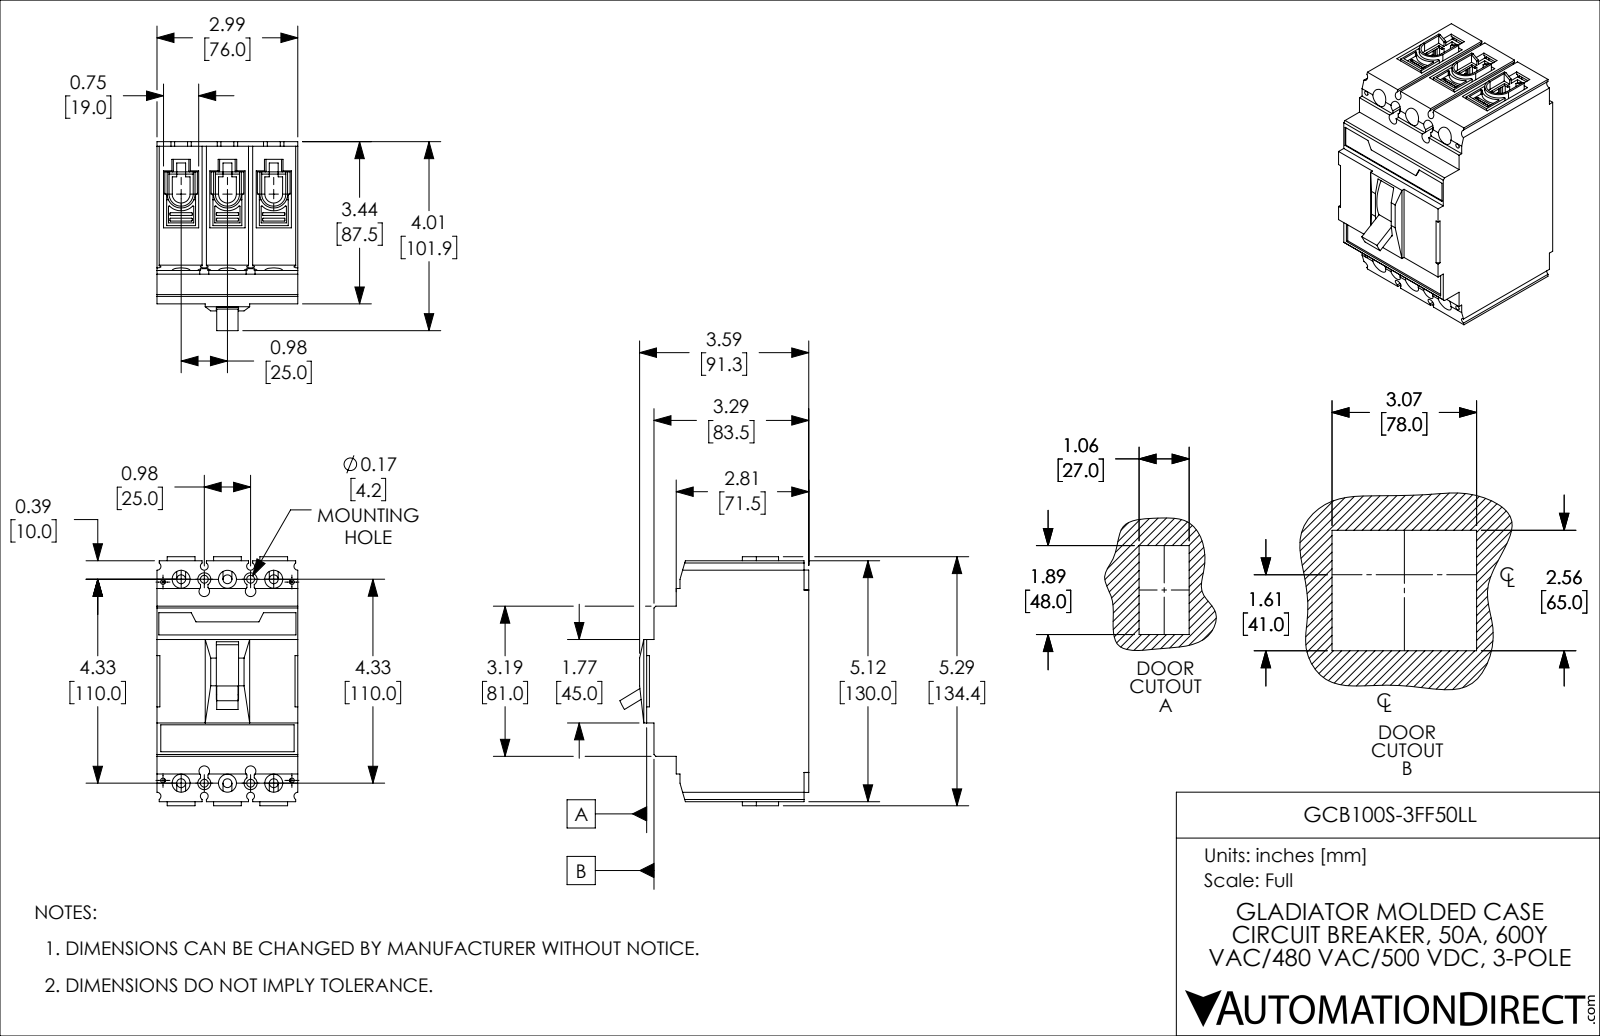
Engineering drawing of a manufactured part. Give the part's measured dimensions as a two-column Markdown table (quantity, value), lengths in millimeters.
| quantity | value |
| --- | --- |
| part name | GCB100S-3FF50LL |
| STEP written by | SolidWorks 2021 (CONFIG_CONTROL_DESIGN) |
| units | millimeters |
| bodies | 1 solid, 1256 faces (784 planar, 424 cylindrical, 48 other) |
| overall size | 134.4 × 101.9 × 76 |
| volume | 708 400 mm³ |
| surface area | 95 810 mm² |
| round holes (diameter × count) | 4.2 × 8, 4.8 × 6, 9.7 × 6, 2.5 × 4, 7 × 4 |
| partial cylindrical surfaces (radius × count) | 0.3 × 86, 0.5 × 38, 1 × 14, 4 × 14, 0.6 × 6, 2.1 × 4, 2.8 × 4, 4.8 × 3 |
| main face-to-face distances | 76, 25, 15.8, 114.2, 44, 2.8, 87.5, 19, 50, 130 |
| hole center spacings | 12.5, 14.3, 25, 110.7, 117.7, 112.8, 110, 7 |
